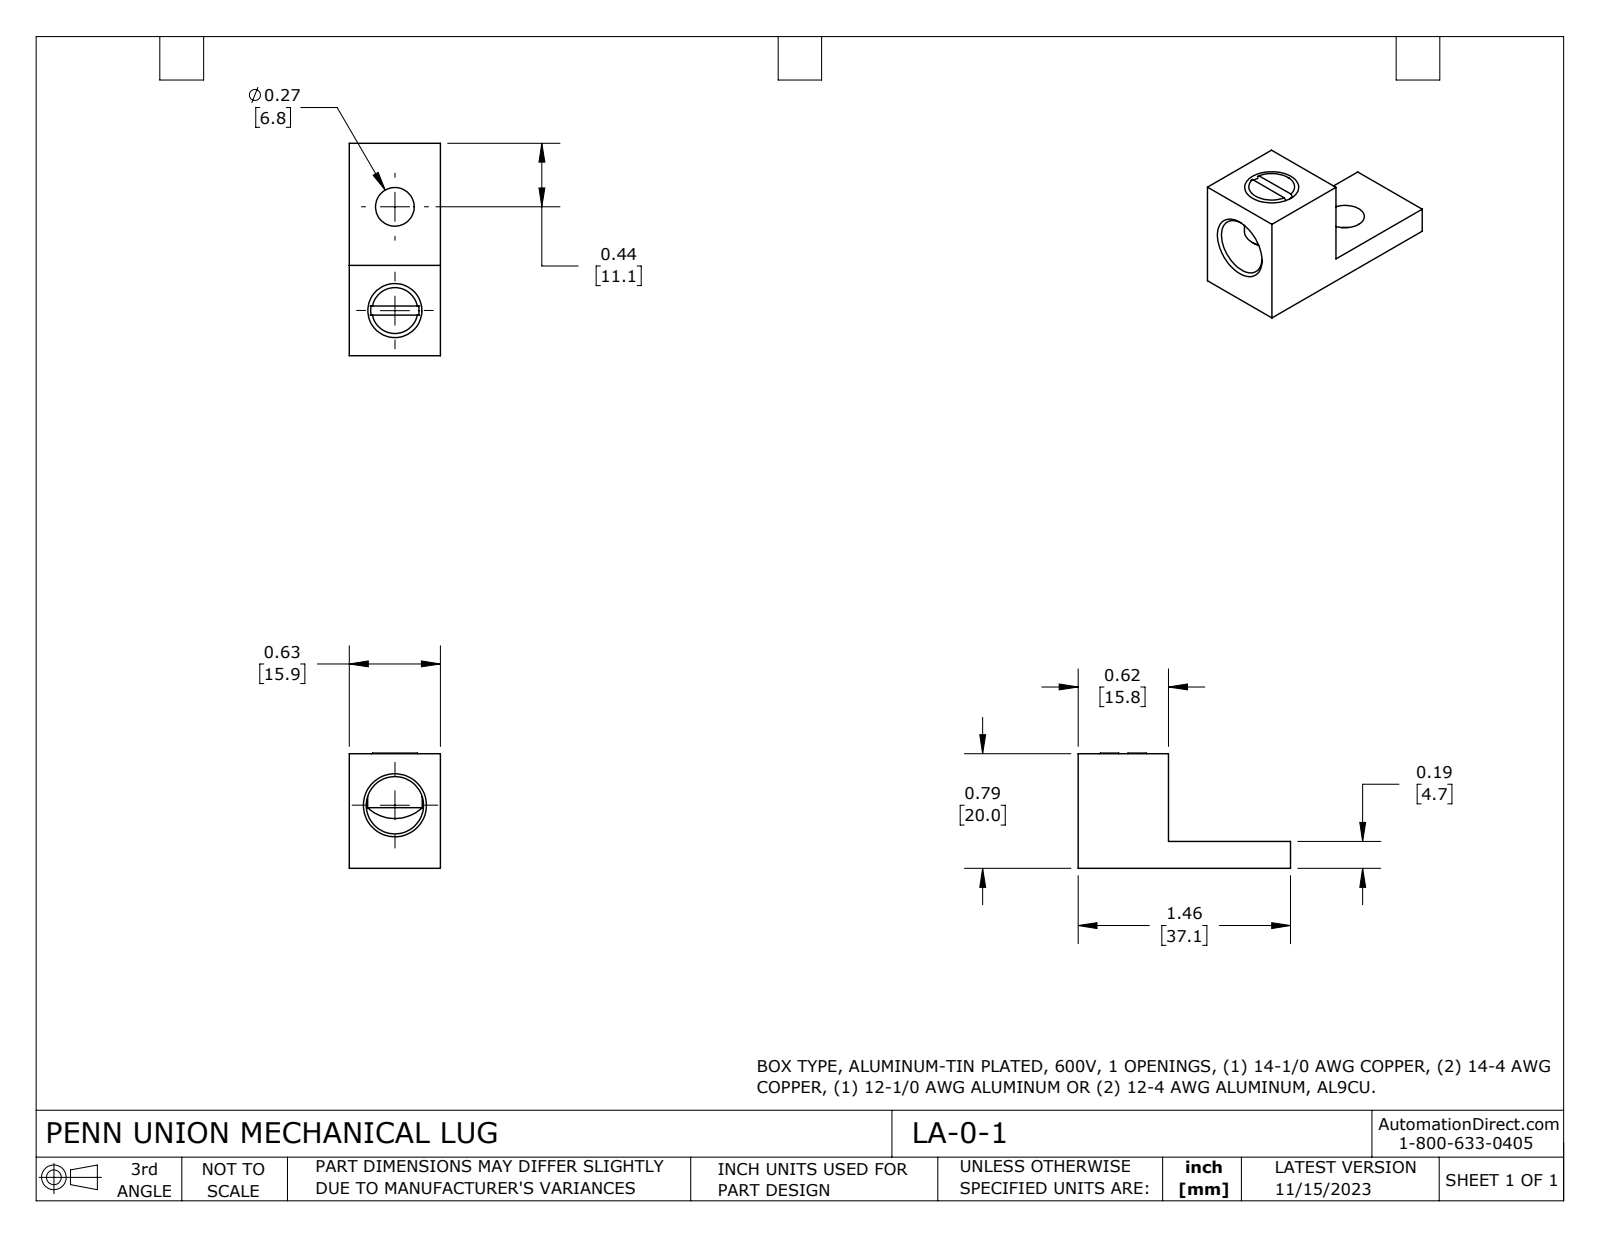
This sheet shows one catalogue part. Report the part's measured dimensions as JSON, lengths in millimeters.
{"part_name": "LA-0-1", "step_written_by": "SolidWorks 2023 (CONFIG_CONTROL_DESIGN)", "units": "millimeters", "bodies": {"solids": 2, "faces": 30, "planar": 13, "cylindrical": 8, "other": 9}, "overall_size": [37.1, 20.1, 15.9], "volume_mm3": 5650, "surface_area_mm2": 3473, "round_holes": [[6.8, 1], [8.4, 1], [10, 1]], "round_bosses_or_shafts": [[9.5, 1]], "face_to_face_distances": [15.9, 4.7, 20, 15.3, 15.8, 37.1, 21.3, 7.1, 8.7, 20.1], "hole_center_spacings": [18.1]}
